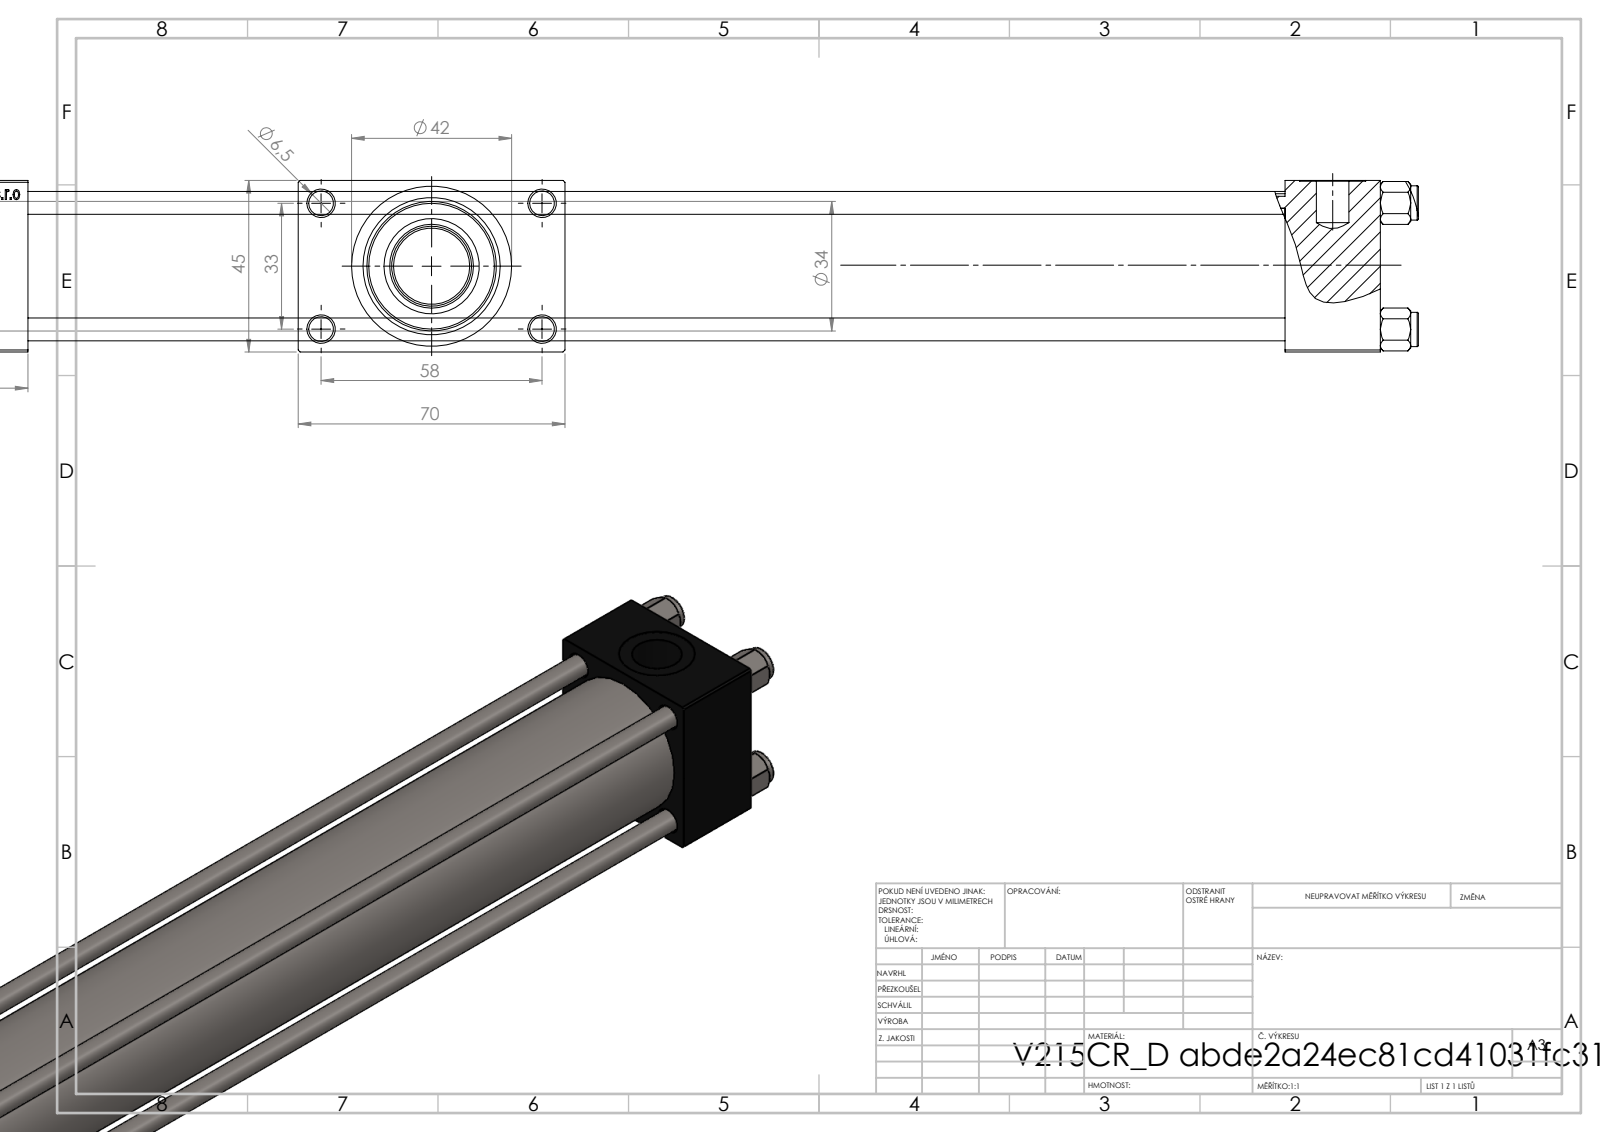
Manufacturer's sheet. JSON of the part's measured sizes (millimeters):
{"part_name": "V215CR_D_TYCINKA; V215CR_D_Body; V215CR_ROD_END_F; V215CR_VCP_D (+2 more)", "step_written_by": "SolidWorks 2019 (CONFIG_CONTROL_DESIGN)", "units": "millimeters", "bodies": {"solids": 12, "faces": 1116, "planar": 499, "cylindrical": 93, "other": 524}, "overall_size": [466, 70, 45], "volume_mm3": 481663, "surface_area_mm2": 183566, "round_holes": [[6, 4], [6.5, 4], [7, 2], [13.16, 2], [20, 2], [10.5, 1], [22, 1], [24, 1], [25, 1], [32, 1], [33, 1]], "round_bosses_or_shafts": [[9, 4], [42, 1], [38, 1], [34, 1], [21, 1], [13, 1]], "face_to_face_distances": [45, 25, 12.5, 57.5, 330, 355, 368, 70, 38, 393], "hole_center_spacings": [12.4, 23.48, 33.2, 33.37, 35.35, 45.6, 56.35, 33]}
